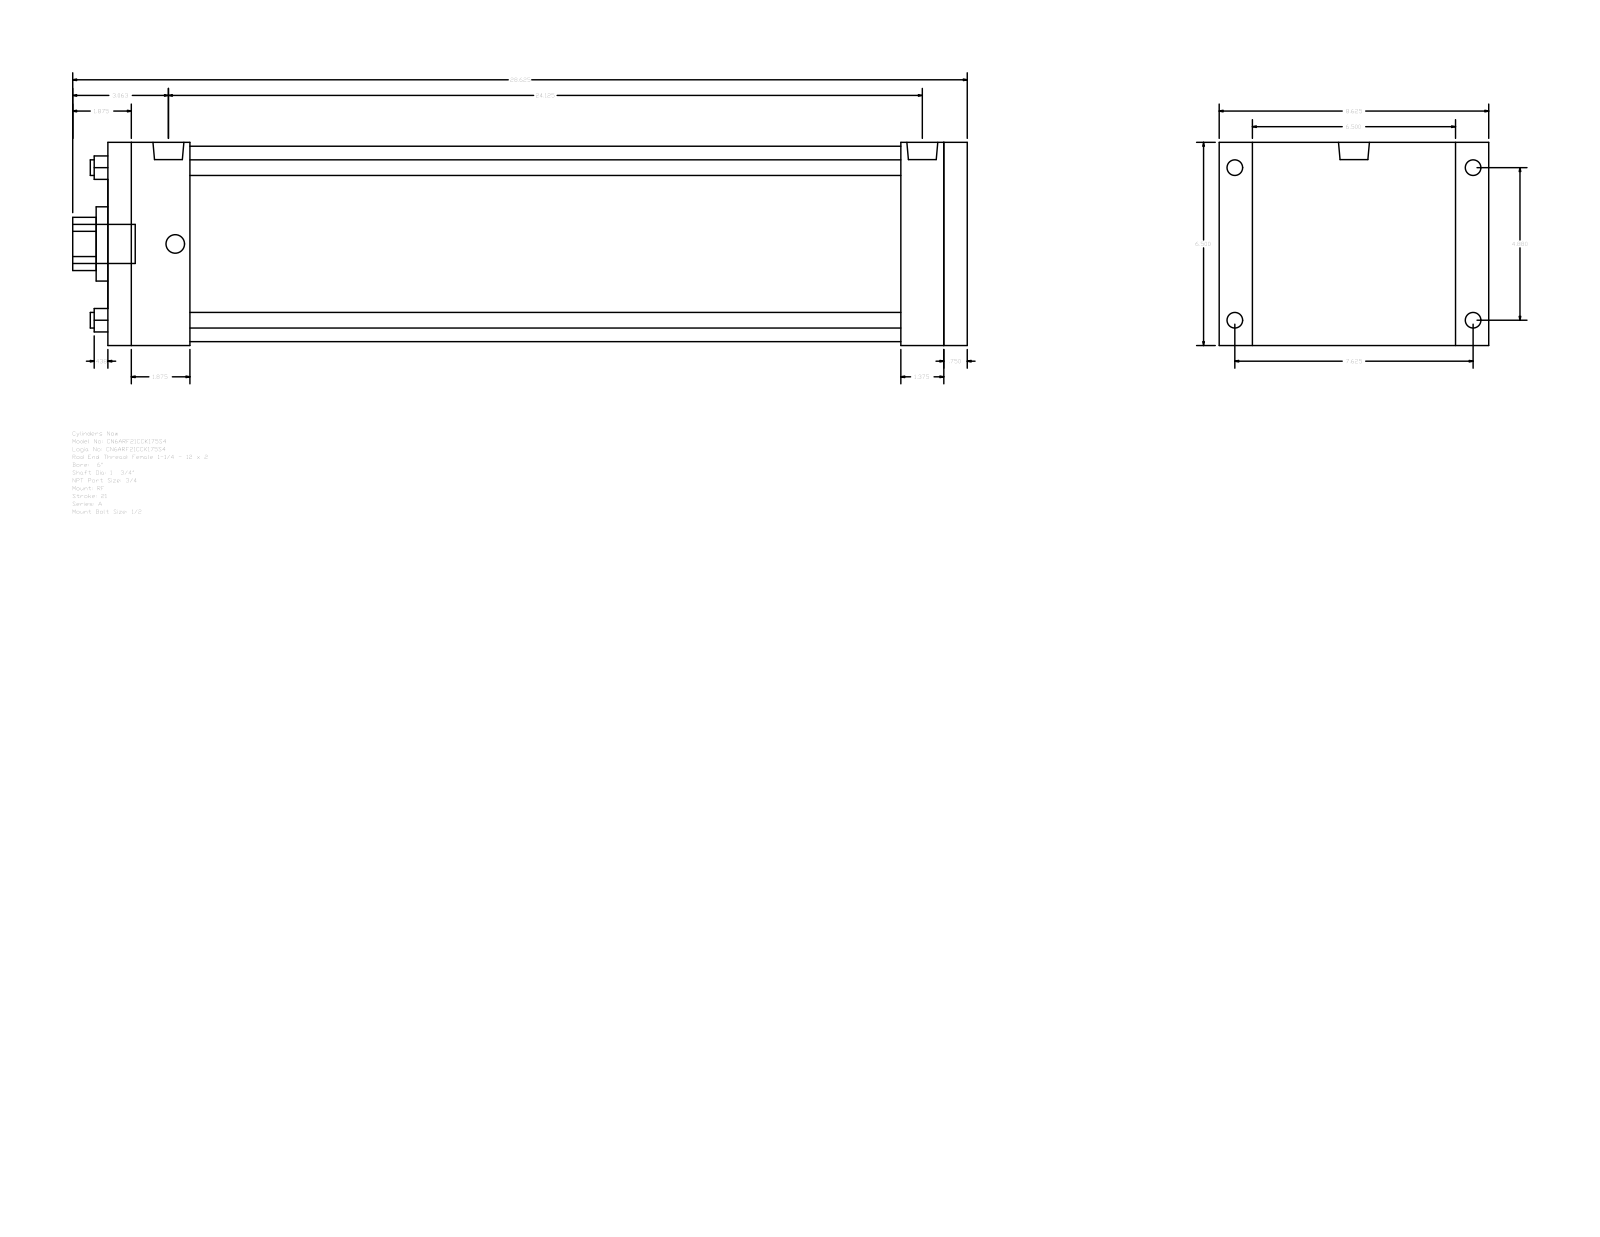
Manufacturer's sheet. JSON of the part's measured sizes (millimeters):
{"part_name": "A_RF__0600_1.75", "step_written_by": "GSSL Pune (CONFIG_CONTROL_DESIGN)", "units": "millimeters", "bodies": {"solids": 0, "faces": 92, "planar": 64, "cylindrical": 28, "other": 0}, "overall_size": [727.08, 219.07, 165.1], "round_holes": [[12.7, 4], [44.45, 1], [60.33, 1], [158.75, 1]], "round_bosses_or_shafts": [[15.08, 4], [12.7, 4], [25.12, 2], [31.75, 1]], "partial_cylinders_radius": [[21.63, 1]], "face_to_face_distances": [165.1, 698.51, 679.45, 19.06, 34.92, 66.68, 612.77, 631.83, 644.53, 577.85], "hole_center_spacings": [87.65, 123.96, 175.31]}
